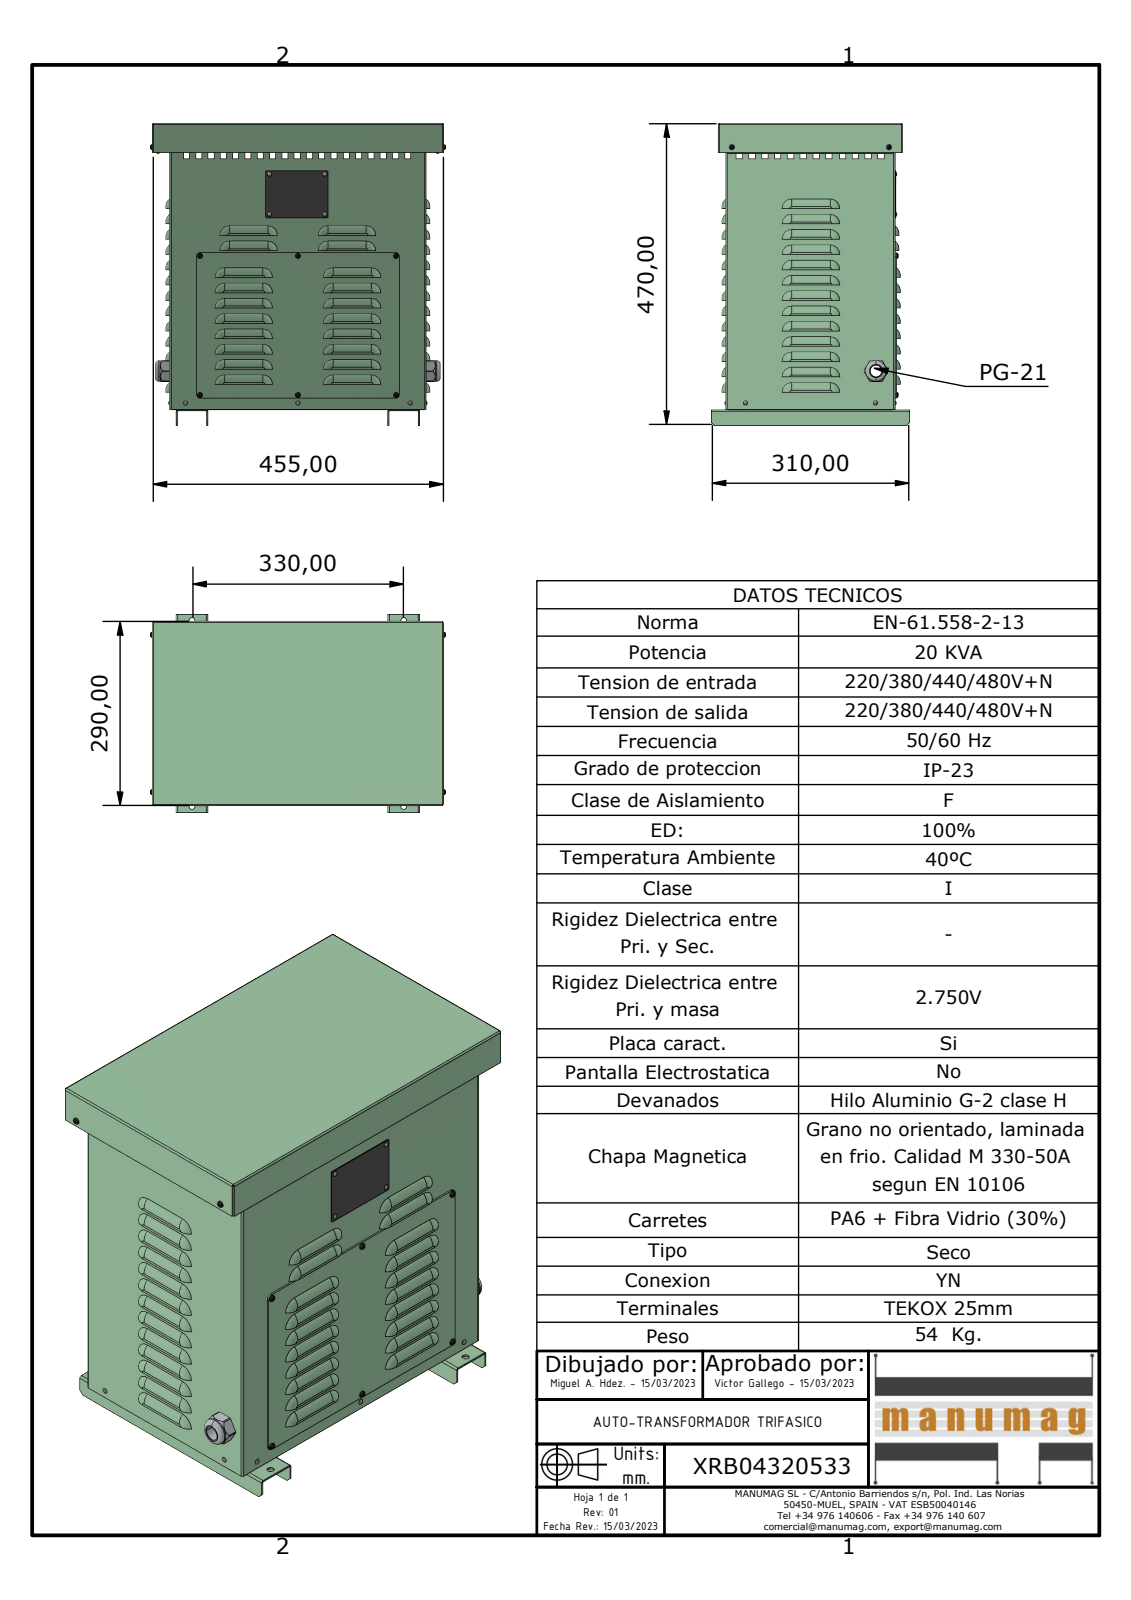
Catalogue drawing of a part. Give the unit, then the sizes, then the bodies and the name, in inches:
Units: inches
Overall size (bounding box): 18.679 × 18.256 × 12.205
Round holes (diameter × count): ⌀0.134 ×17, ⌀0.157 ×9, ⌀0.091 ×8, ⌀0.354 ×6, ⌀0.201 ×3, ⌀0.351 ×2, ⌀0.709 ×1, ⌀1.177 ×1
Round bosses / shafts (diameter × count): ⌀0.126 ×9, ⌀0.157 ×8, ⌀0.143 ×8, ⌀1.276 ×1, ⌀1.122 ×1, ⌀1.114 ×1
Partial cylindrical surfaces — rounded edges, fillets, slot ends (radius × count): R0.551 ×118, R0.157 ×63, R0.591 ×49, R0.079 ×10, R0.079 ×9, R0.137 ×8, R0.02 ×6, R0.098 ×6
Main face-to-face distances: 0.079, 10.351, 10.43, 15.78, 17.609, 17.688, 10.272, 15.701, 15.858, 0.157
Hole centre spacings: 8.587, 6.055, 6.067, 10.507, 10.514, 12.122, 13.082, 14.855
Volume: 142.9 in³ · Surface area: 3 252 in²
Bodies: 33 solids, 2242 faces (1225 planar, 489 cylindrical, 528 other)
Part name (STEP PRODUCT): XRB04320533; JE015 - JE020 - JE025 EXPORT CUERPO; JE015 - JE020 - JE025 EXPORT BASE; JE015 - JE020 - JE025 EXPORT PATA (+6 more)
STEP written by: Autodesk Inventor 2023 (AUTOMOTIVE_DESIGN)
